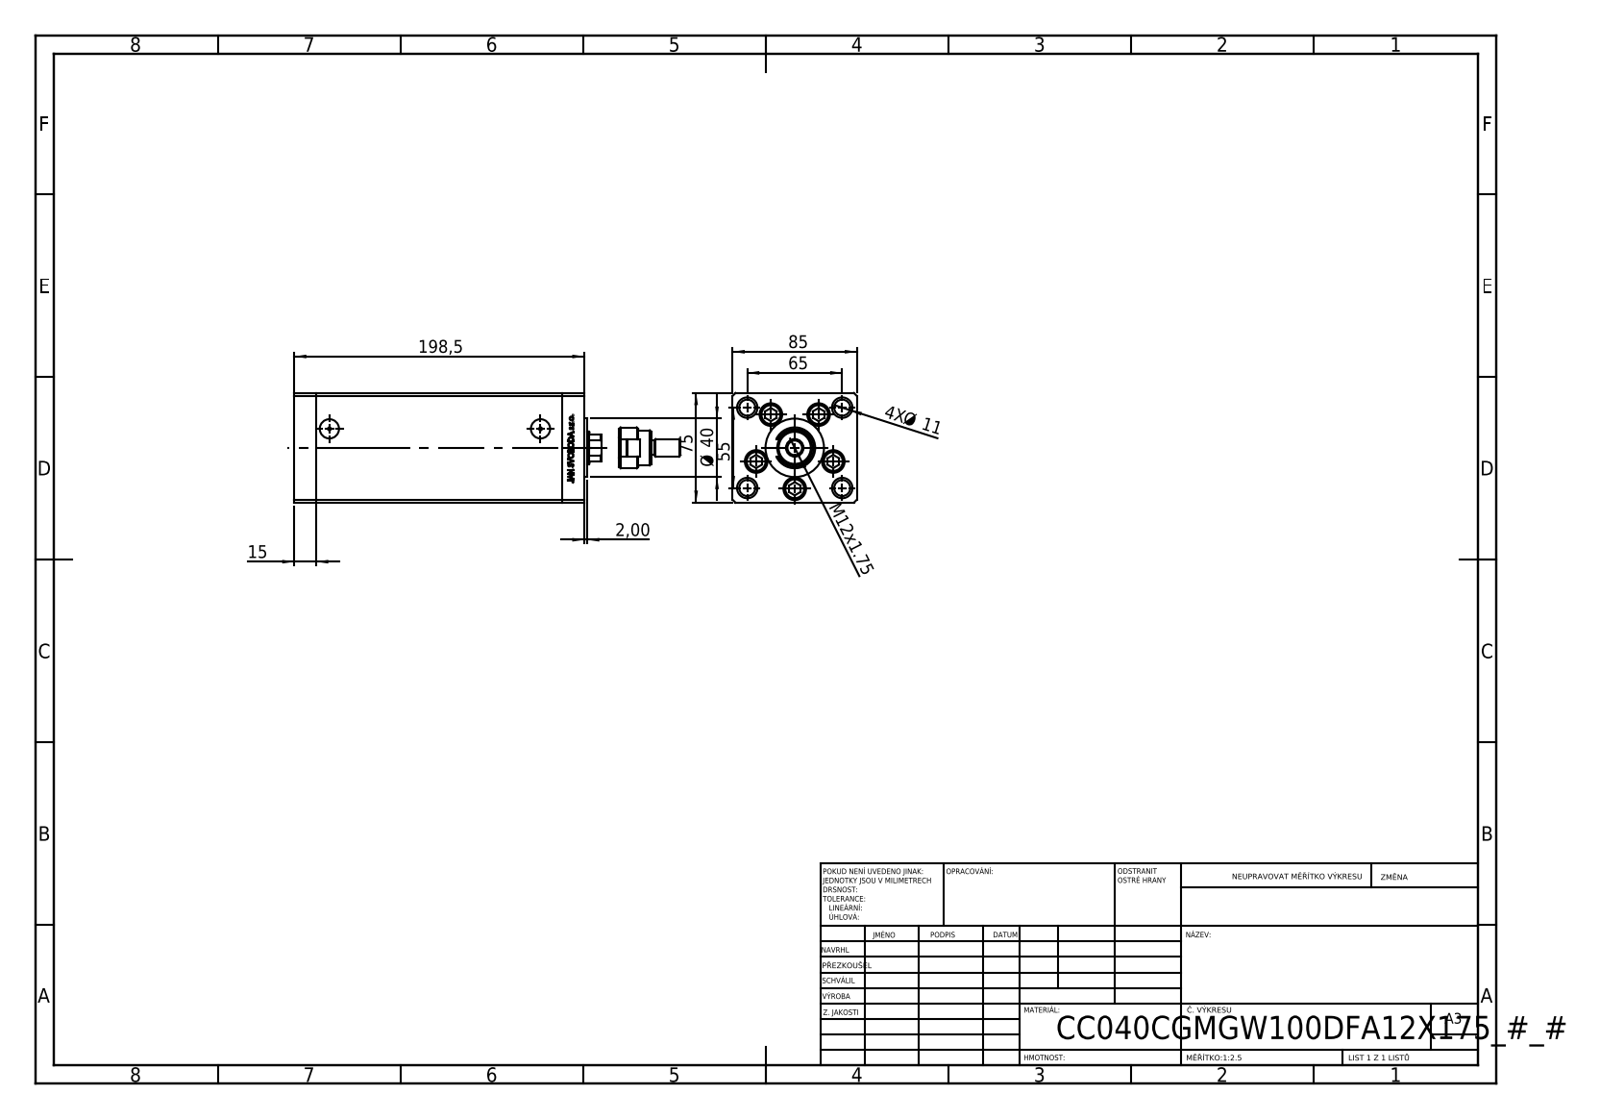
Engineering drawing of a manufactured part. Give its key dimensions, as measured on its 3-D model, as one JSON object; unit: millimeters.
{"part_name": "V220C BACK_C; V220C_C MIDDLE; ALLEN BOLT; V220C_VC_C (+2 more)", "step_written_by": "SolidWorks 2019 (CONFIG_CONTROL_DESIGN)", "units": "millimeters", "bodies": {"solids": 14, "faces": 1208, "planar": 558, "cylindrical": 176, "other": 474}, "overall_size": [264.3, 85, 75], "volume_mm3": 1055000, "surface_area_mm2": 198507, "round_holes": [[11, 9], [15.5, 5], [10, 4], [14, 4], [2, 2], [13.16, 2], [13.5, 1], [14.5, 1], [22, 1]], "round_bosses_or_shafts": [[8, 5], [14.5, 4], [40, 1], [28, 1], [24, 1], [12, 1], [10, 1]], "partial_cylinders_radius": [[0.93, 2], [9.75, 1], [10.5, 1]], "face_to_face_distances": [85, 75, 168.5, 15, 183.5, 10.5, 198.5, 34.25, 68.5, 164.25], "hole_center_spacings": [28, 42.57, 16.86, 19.17, 32.33, 32.5, 33.63, 37.33]}
